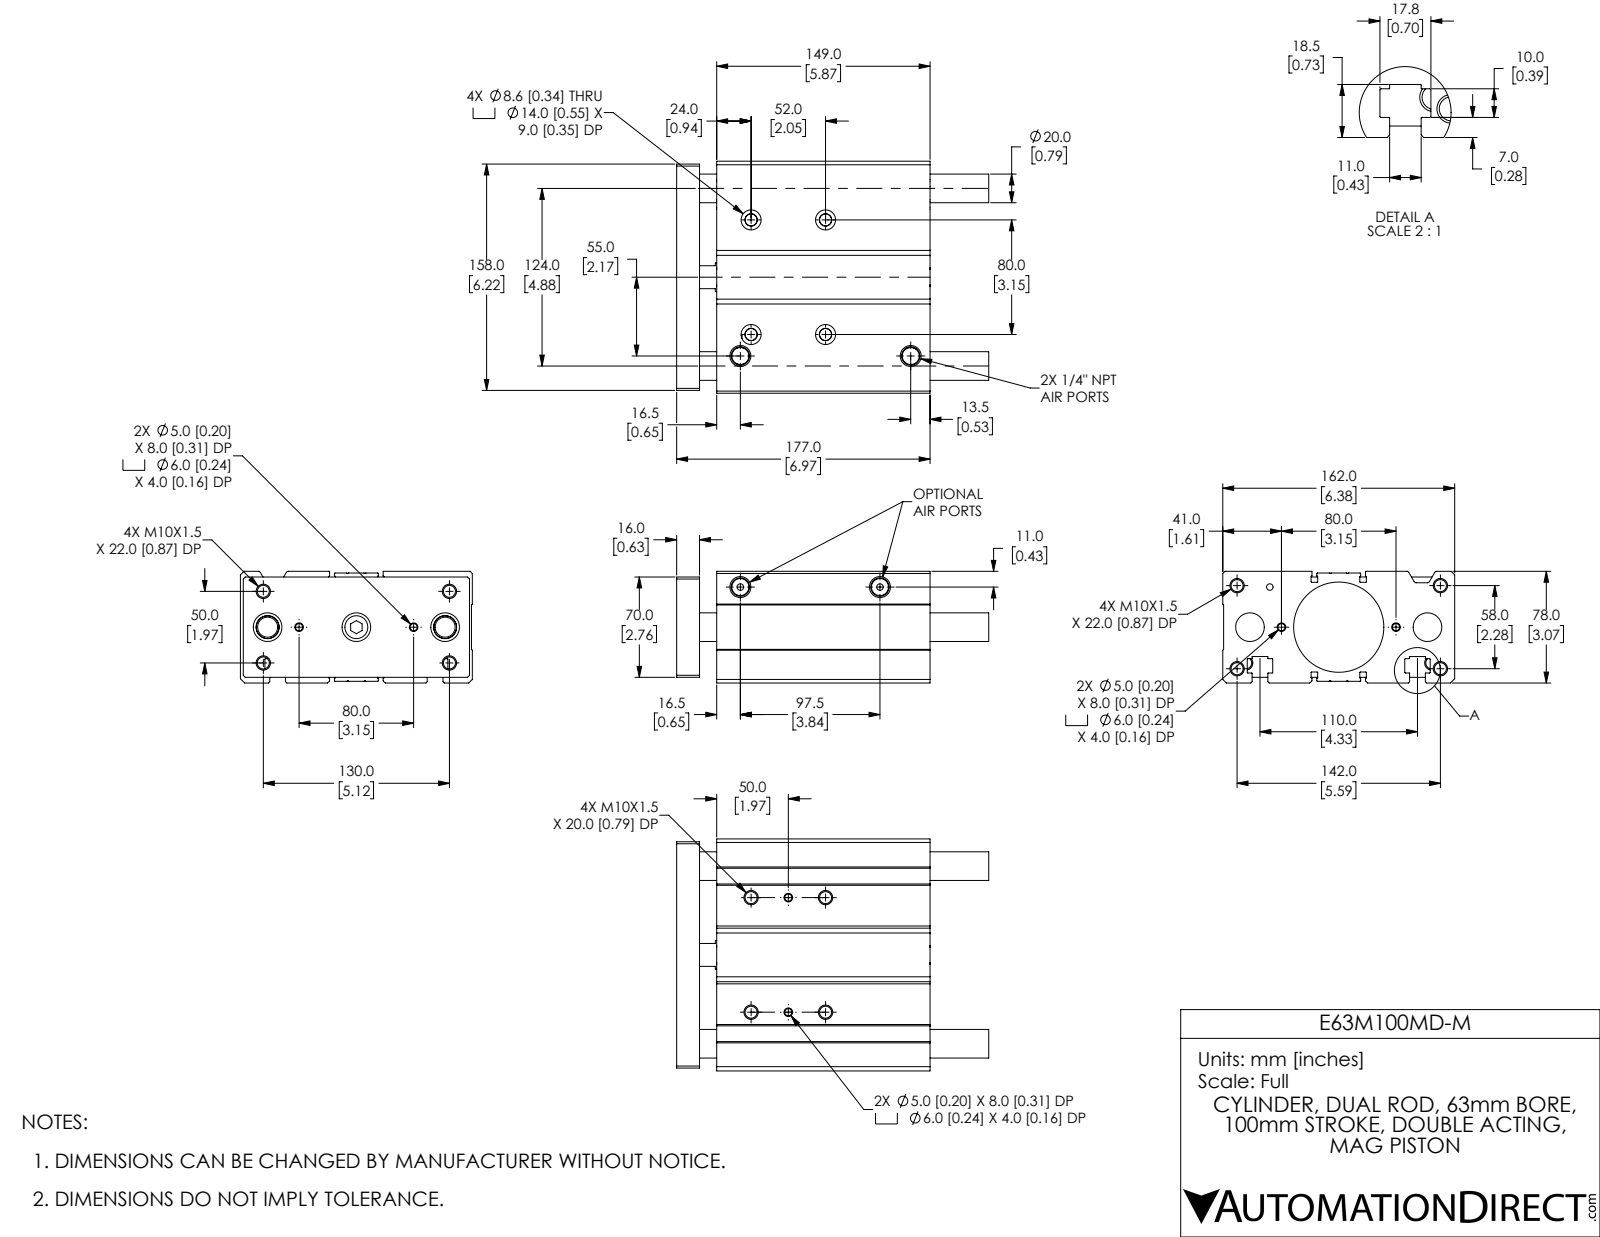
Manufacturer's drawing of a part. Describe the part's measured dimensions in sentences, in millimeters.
The part is named "E63M100MD-M; E63M100MD-M_BODY; E63M100MD-M_ENDPLATE". Its 3-D file was written by "SolidWorks 2019 (CONFIG_CONTROL_DESIGN)". It is 5 solids with 421 faces: 139 planar, 190 cylindrical and 92 other. Overall it measures 218 by 162 by 78 millimeters. Its volume is 1 636 000 cubic millimeters and its surface area 266 913 square millimeters. Round holes: 12 of diameter 8.38, 4 of diameter 5, 4 of diameter 6, 4 of diameter 8.6, 4 of diameter 14, 3 of diameter 4.57, 3 of diameter 10, 3 of diameter 20, 2 of diameter 16, 1 of diameter 20, 1 of diameter 63, 1 of diameter 63. Round bosses or shafts: 1 of diameter 16. Partial cylindrical surfaces (rounded edges, fillets, slot ends): 32 of radius 0.2, 28 of radius 0.4, 4 of radius 1.5, 2 of radius 0.3. The main face-to-face distances are 78, 28, 16, 12, 1.2, 76.8, 4, 177, 161, 149. The hole center spacings are 7.21, 25.18, 26, 30.36, 35.36, 42.45, 54.33, 69.64.
